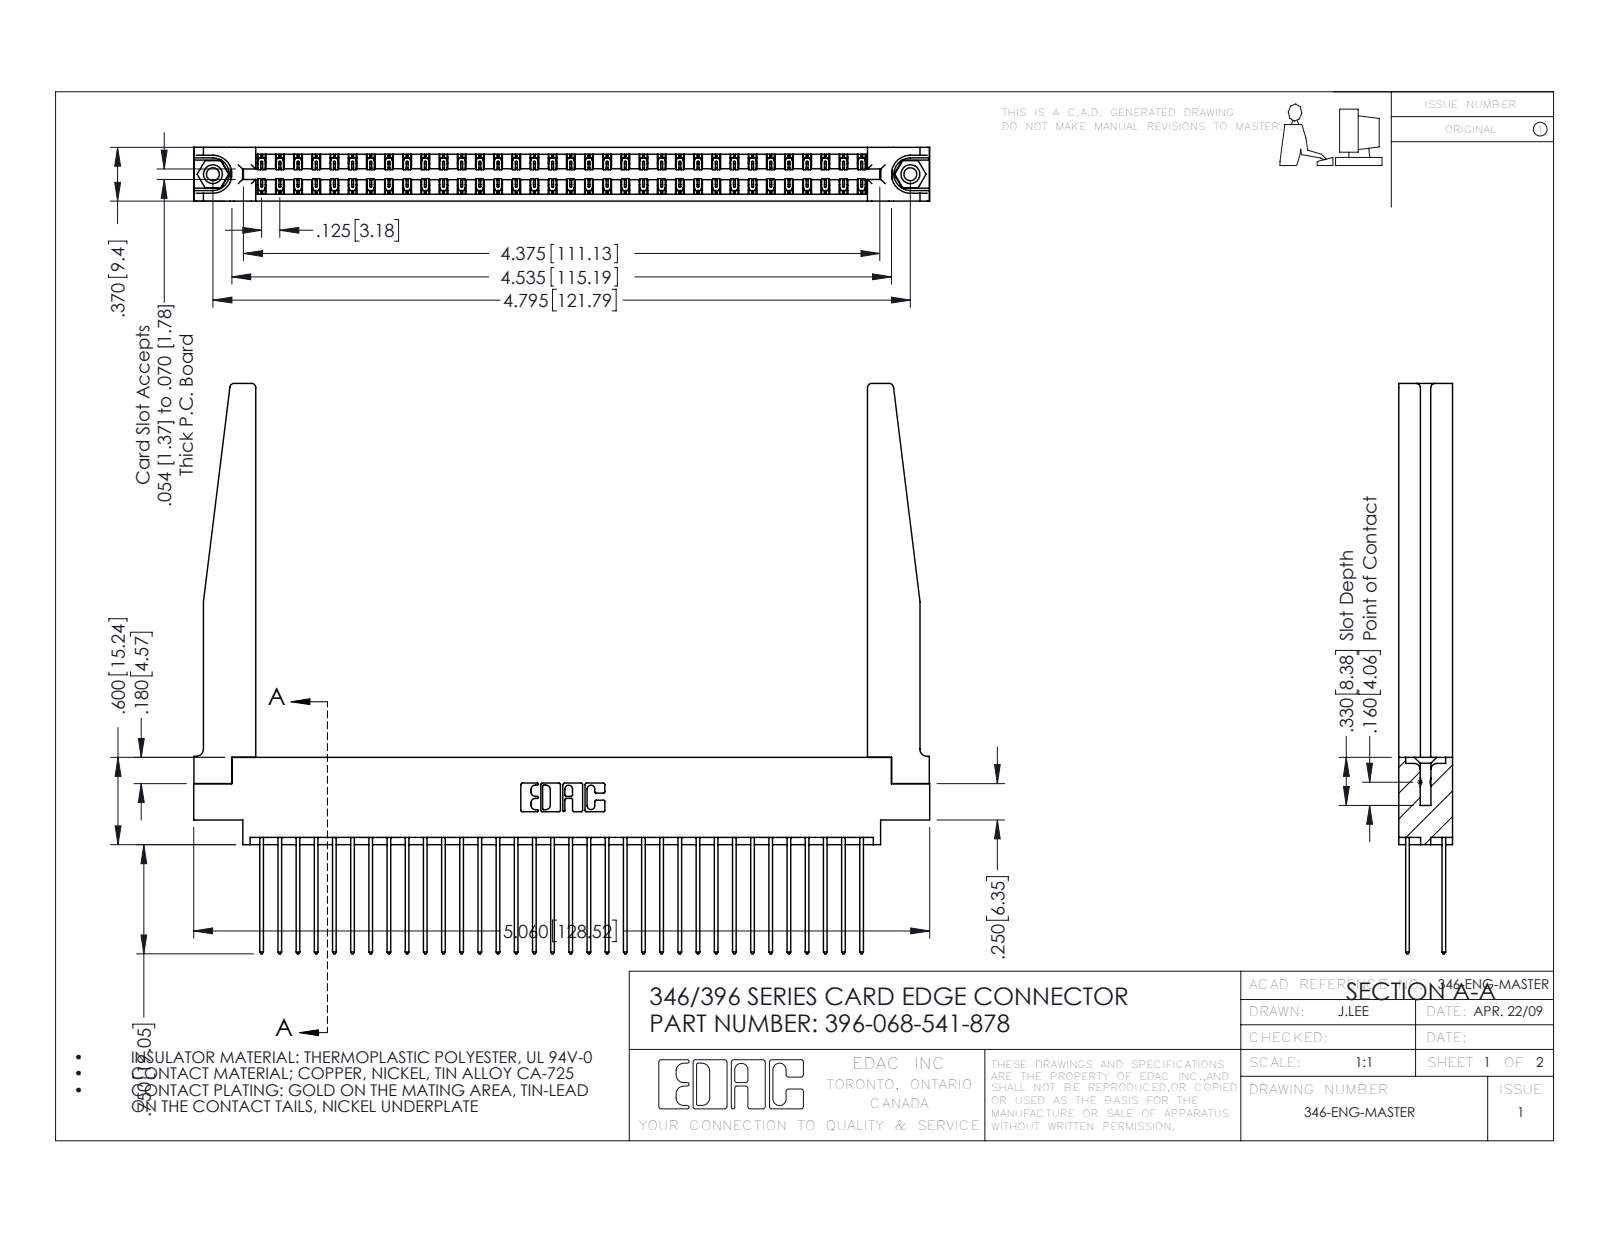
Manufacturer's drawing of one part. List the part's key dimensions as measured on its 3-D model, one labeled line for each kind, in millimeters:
Part name (STEP PRODUCT): 346 Part_0.170 Offset - 0.156 Dia-TH; 396-068-541-878; 345-292-001_345-293-141; 345-250-001_345-250-001-102 (+1 more)
STEP written by: SolidWorks 2016 (CONFIG_CONTROL_DESIGN)
Units: millimetres
Bodies: 73 solids, 3896 faces (2602 planar, 1242 cylindrical, 52 other)
Overall size (bounding box): 128.5 × 99.6 × 9.4
Volume: 19 620 mm³ · Surface area: 25 930 mm²
Round holes (diameter × count): ⌀2.3 ×2, ⌀3.2 ×2, ⌀4 ×2, ⌀1.6 ×1
Round bosses / shafts (diameter × count): ⌀3.9 ×2
Partial cylindrical surfaces — rounded edges, fillets, slot ends (radius × count): R0.2 ×102, R0.3 ×68, R0.3 ×22, R0.8 ×8, R0.2 ×6, R0.8 ×6, R0.7 ×3, R0.4 ×2
Main face-to-face distances: 1.2, 8.2, 9.4, 1.8, 6.4, 7.6, 0.6, 3.8, 3.8, 7
Hole centre spacings: 6.2, 116.5, 121.8
